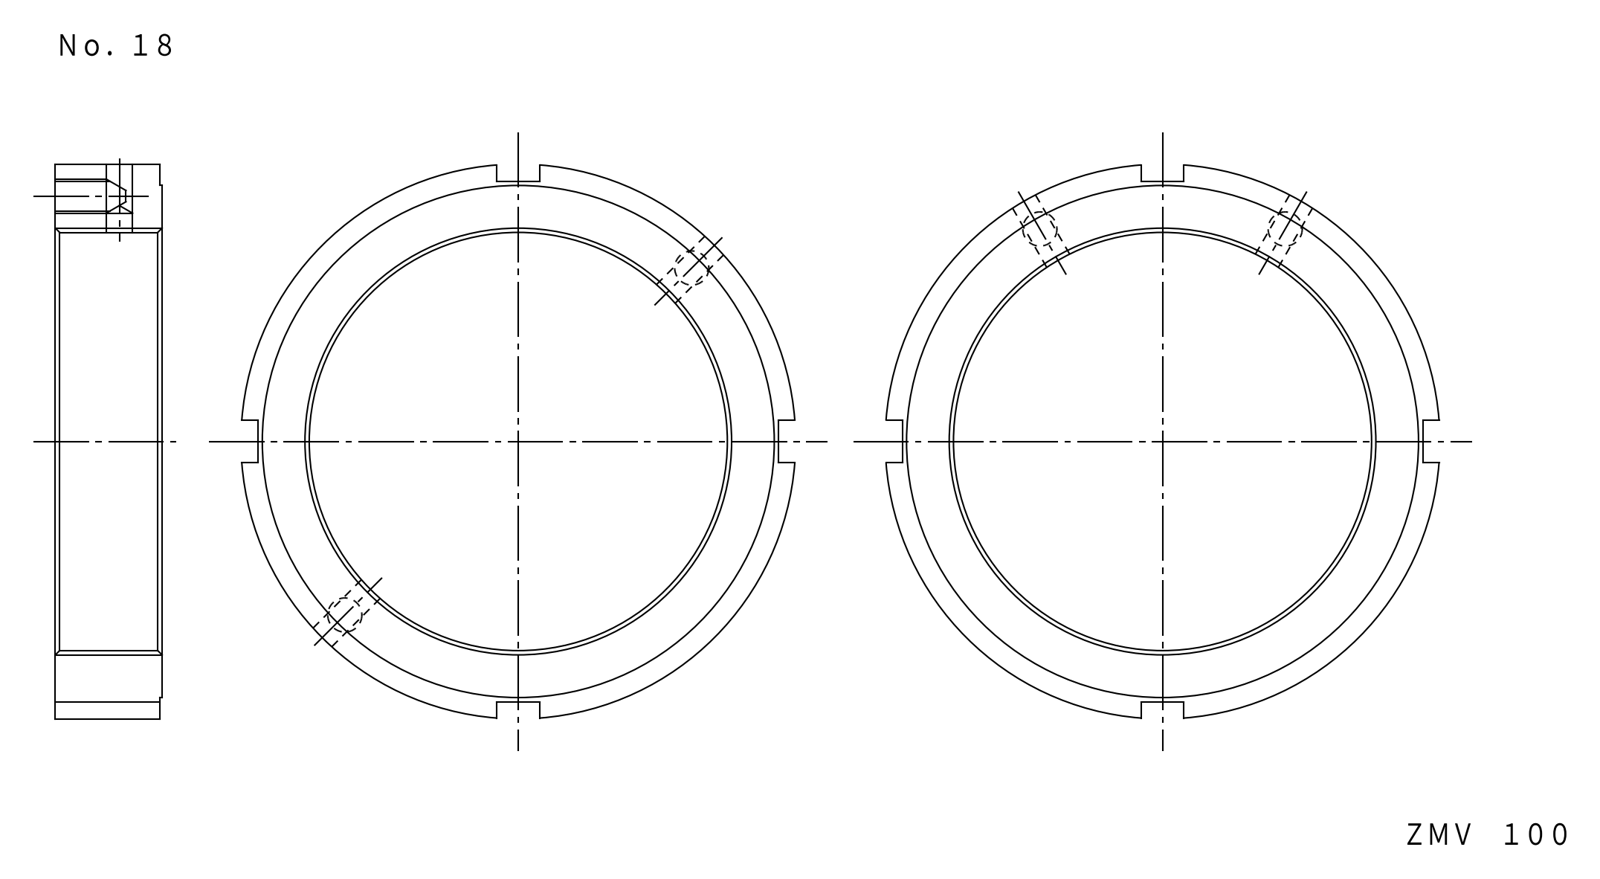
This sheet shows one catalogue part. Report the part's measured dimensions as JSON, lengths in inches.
{"part_name": "FKD ZMV100", "step_written_by": "Autodesk Inventor LT (CONFIG_CONTROL_DESIGN)", "units": "inches", "bodies": {"solids": 1, "faces": 29, "planar": 15, "cylindrical": 10, "other": 4}, "overall_size": [5.103, 5.103, 0.984], "volume_in3": 7.864, "surface_area_in2": 46.77, "round_holes": [[0.244, 2], [0.262, 2], [3.937, 1]], "round_bosses_or_shafts": [[5.118, 1], [4.724, 1]], "face_to_face_distances": [0.984, 0.02, 0.965, 2.205, 2.598, 4.803, 0.394], "hole_center_spacings": [2.264, 4.528]}
